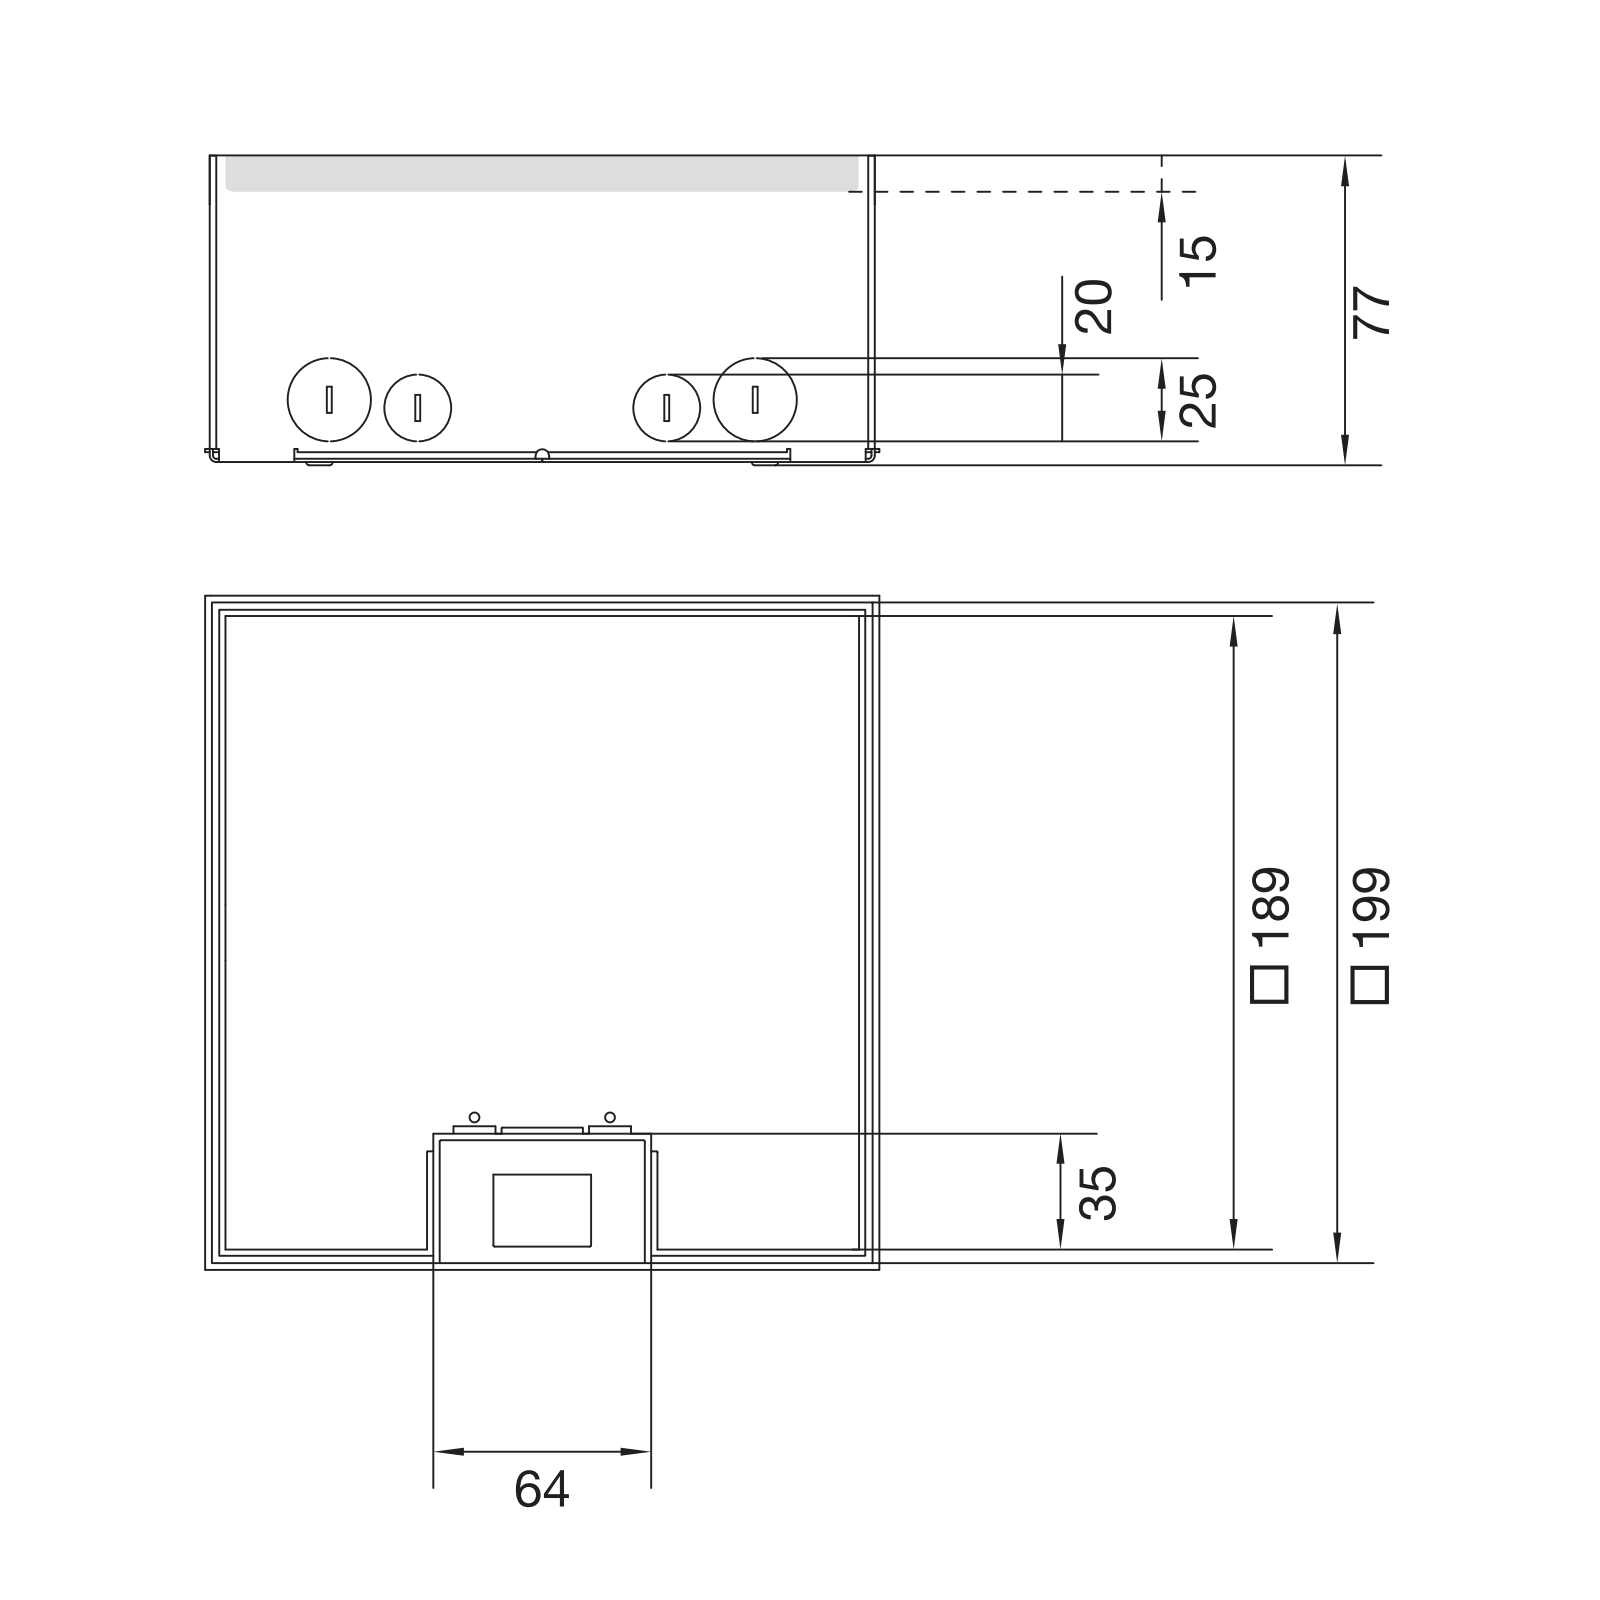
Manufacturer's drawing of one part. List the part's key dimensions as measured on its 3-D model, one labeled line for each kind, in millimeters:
Part name (STEP PRODUCT): T-00658; 60449-M; 60450-M; T-00714 (+8 more)
STEP written by: CREO PARAMETRIC BY PTC INC, 2022024 (AUTOMOTIVE_DESIGN)
Units: millimetres
Bodies: 28 solids, 1462 faces (915 planar, 329 cylindrical, 218 other)
Overall size (bounding box): 203.25 × 203 × 76
Volume: 410 931 mm³ · Surface area: 547 125 mm²
Round holes (diameter × count): ⌀20.4 ×12, ⌀25.4 ×8, ⌀6.8 ×4, ⌀7.5 ×4, ⌀18.5 ×4, ⌀2.7 ×2
Round bosses / shafts (diameter × count): ⌀20 ×16, ⌀25 ×8, ⌀20.5 ×4, ⌀12 ×4, ⌀11.5 ×4, ⌀9.85 ×4, ⌀8.5 ×4, ⌀8 ×4
Partial cylindrical surfaces — rounded edges, fillets, slot ends (radius × count): R1 ×21, R5 ×16, R3 ×12, R2.1 ×8, R2 ×7, R2.25 ×6, R105 ×5, R6.6 ×1
Main face-to-face distances: 1, 2, 202, 3, 5, 201, 59, 60, 58, 61
Hole centre spacings: 27.12, 71.94, 103.03, 171, 27.23, 41.72, 42.43, 43.14
